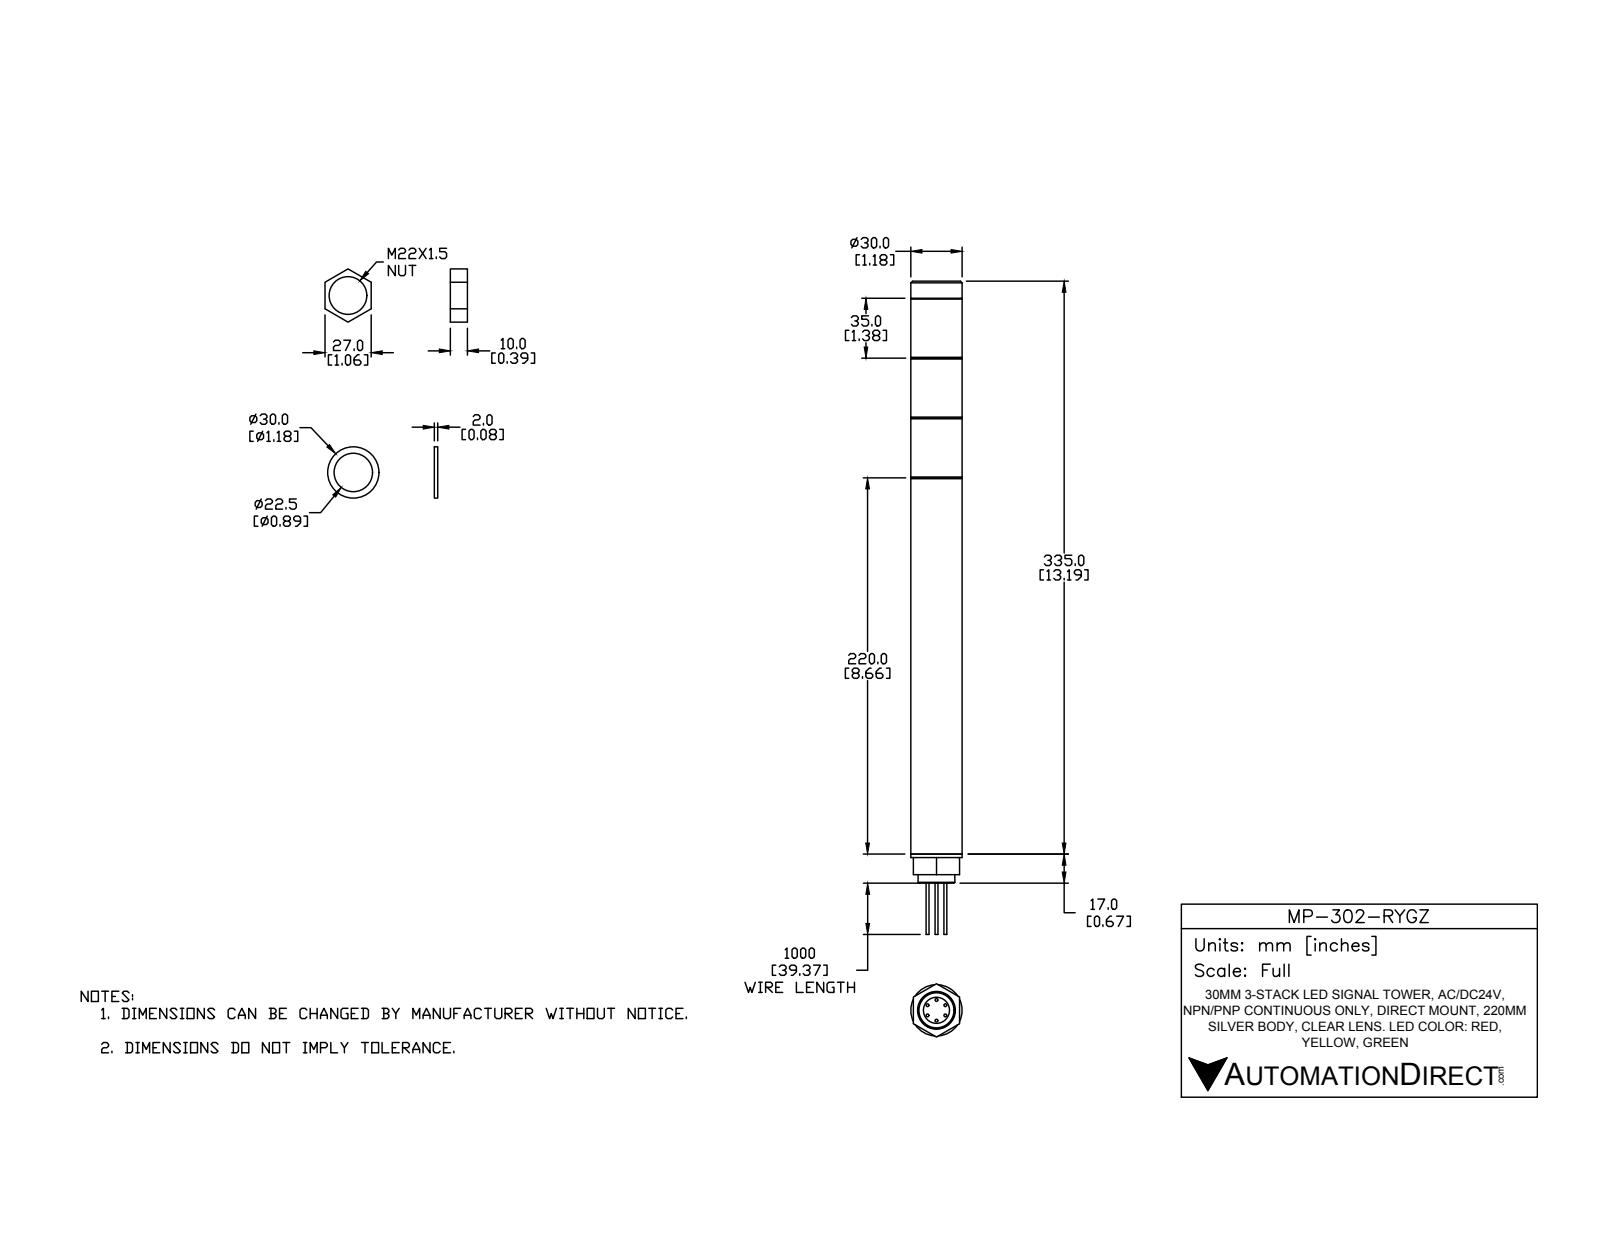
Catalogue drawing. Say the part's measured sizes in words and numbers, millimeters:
The part is named "MP-302-RYGZ". Its 3-D file was written by "SolidWorks 2016 (AUTOMOTIVE_DESIGN)". It is 14 solids with 111 faces: 51 planar, 40 cylindrical and 20 other. Overall it measures 382 by 31.18 by 30 millimeters. Its volume is 232 734 cubic millimeters and its surface area 48 731 square millimeters. Round holes: 1 of diameter 3.2, 1 of diameter 7.7, 1 of diameter 15.3, 1 of diameter 20.7, 1 of diameter 22. Round bosses or shafts: 6 of diameter 1.7, 1 of diameter 30, 1 of diameter 21.5, 1 of diameter 5. The main face-to-face distances are 35, 70, 105, 222, 257, 292, 45, 337, 220, 255.
